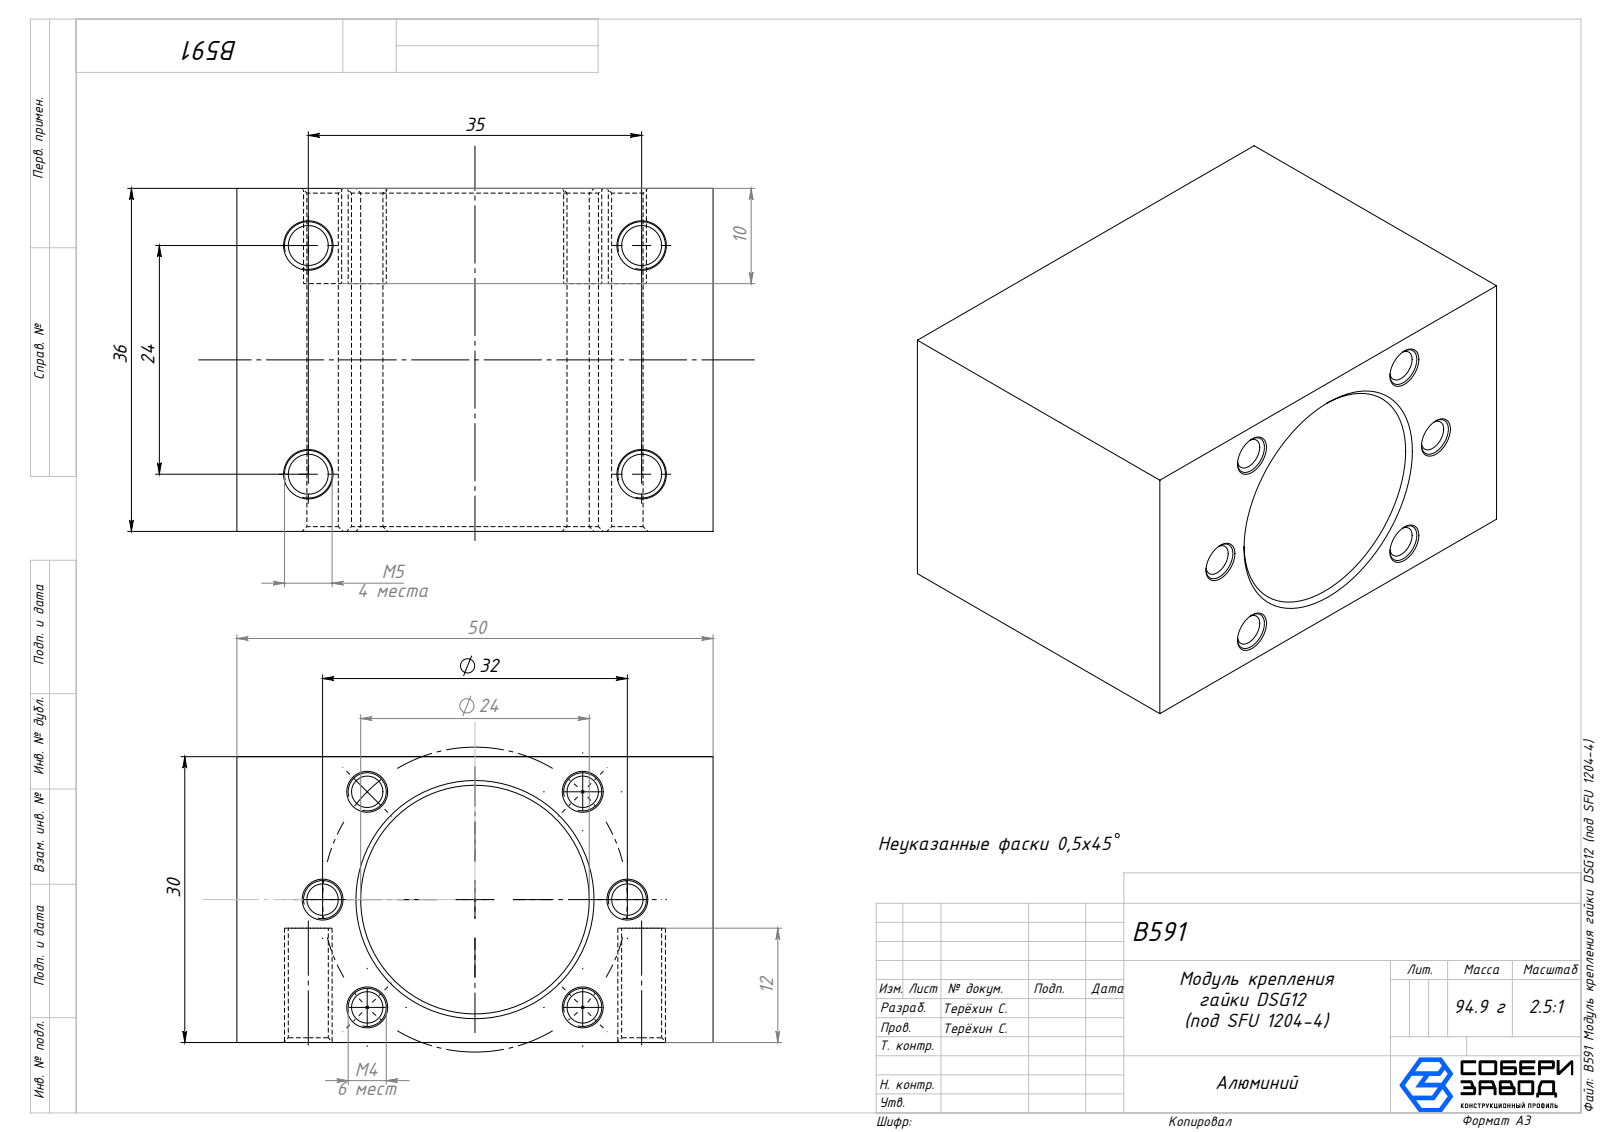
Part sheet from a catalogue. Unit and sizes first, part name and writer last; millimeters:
Units: millimetres
Overall size (bounding box): 50 × 36 × 30
Round holes (diameter × count): ⌀3.3 ×6, ⌀4.2 ×4, ⌀22 ×1
Main face-to-face distances: 30, 50, 36, 12, 18
Hole centre spacings: 12.24, 15.99, 22.62, 29.56, 16, 24, 31.99, 35
Volume: 37 761 mm³ · Surface area: 13 171 mm²
Bodies: 1 solid, 68 faces (10 planar, 22 cylindrical, 36 other)
Part name (STEP PRODUCT): B591 Модуль крепления гайки DSG12 (под SFU 1204-4); B591 Модуль крепления гайки DSG12 (под SFU 1204-4)_00
STEP written by: SolidWorks 2025 (CONFIG_CONTROL_DESIGN)
